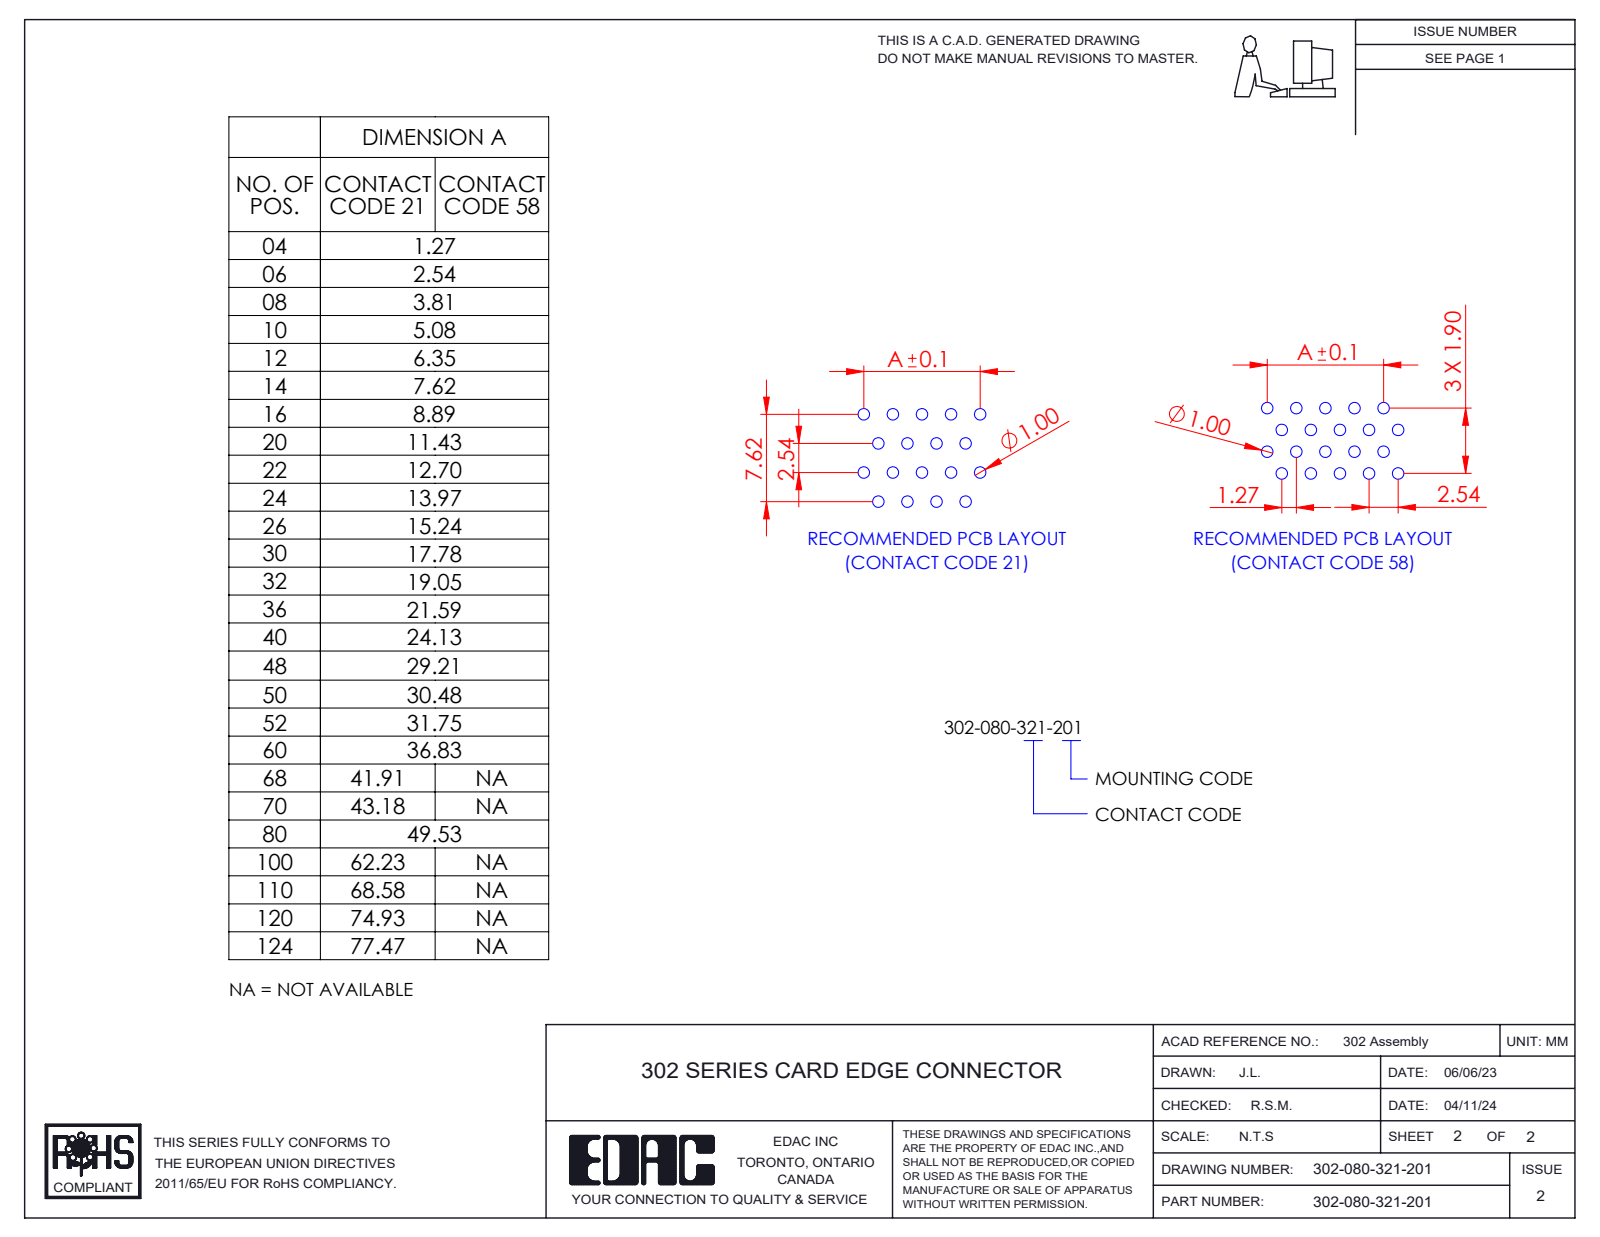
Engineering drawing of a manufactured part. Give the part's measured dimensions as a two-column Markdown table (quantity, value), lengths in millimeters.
| quantity | value |
| --- | --- |
| part name | Contact_302-290-X21 (2); HSG_Vertical HSG; Contact_302-290-X21 (1); 302-080-321-201 |
| STEP written by | SolidWorks 2023 (CONFIG_CONTROL_DESIGN) |
| units | millimeters |
| bodies | 81 solids, 3706 faces (2729 planar, 813 cylindrical, 164 other) |
| overall size | 56.9 × 17.63 × 8.88 |
| volume | 4 394 mm³ |
| surface area | 12 188 mm² |
| partial cylindrical surfaces (radius × count) | 0.2 × 88, 2.03 × 4, 2.09 × 4, 0.11 × 2, 0.4 × 2, 0.41 × 2, 1.25 × 2, 1.53 × 2 |
| main face-to-face distances | 2.54, 1.27, 5.08, 3.81, 7.62, 6.35, 8.88, 8.89, 10.16, 11.43 |
